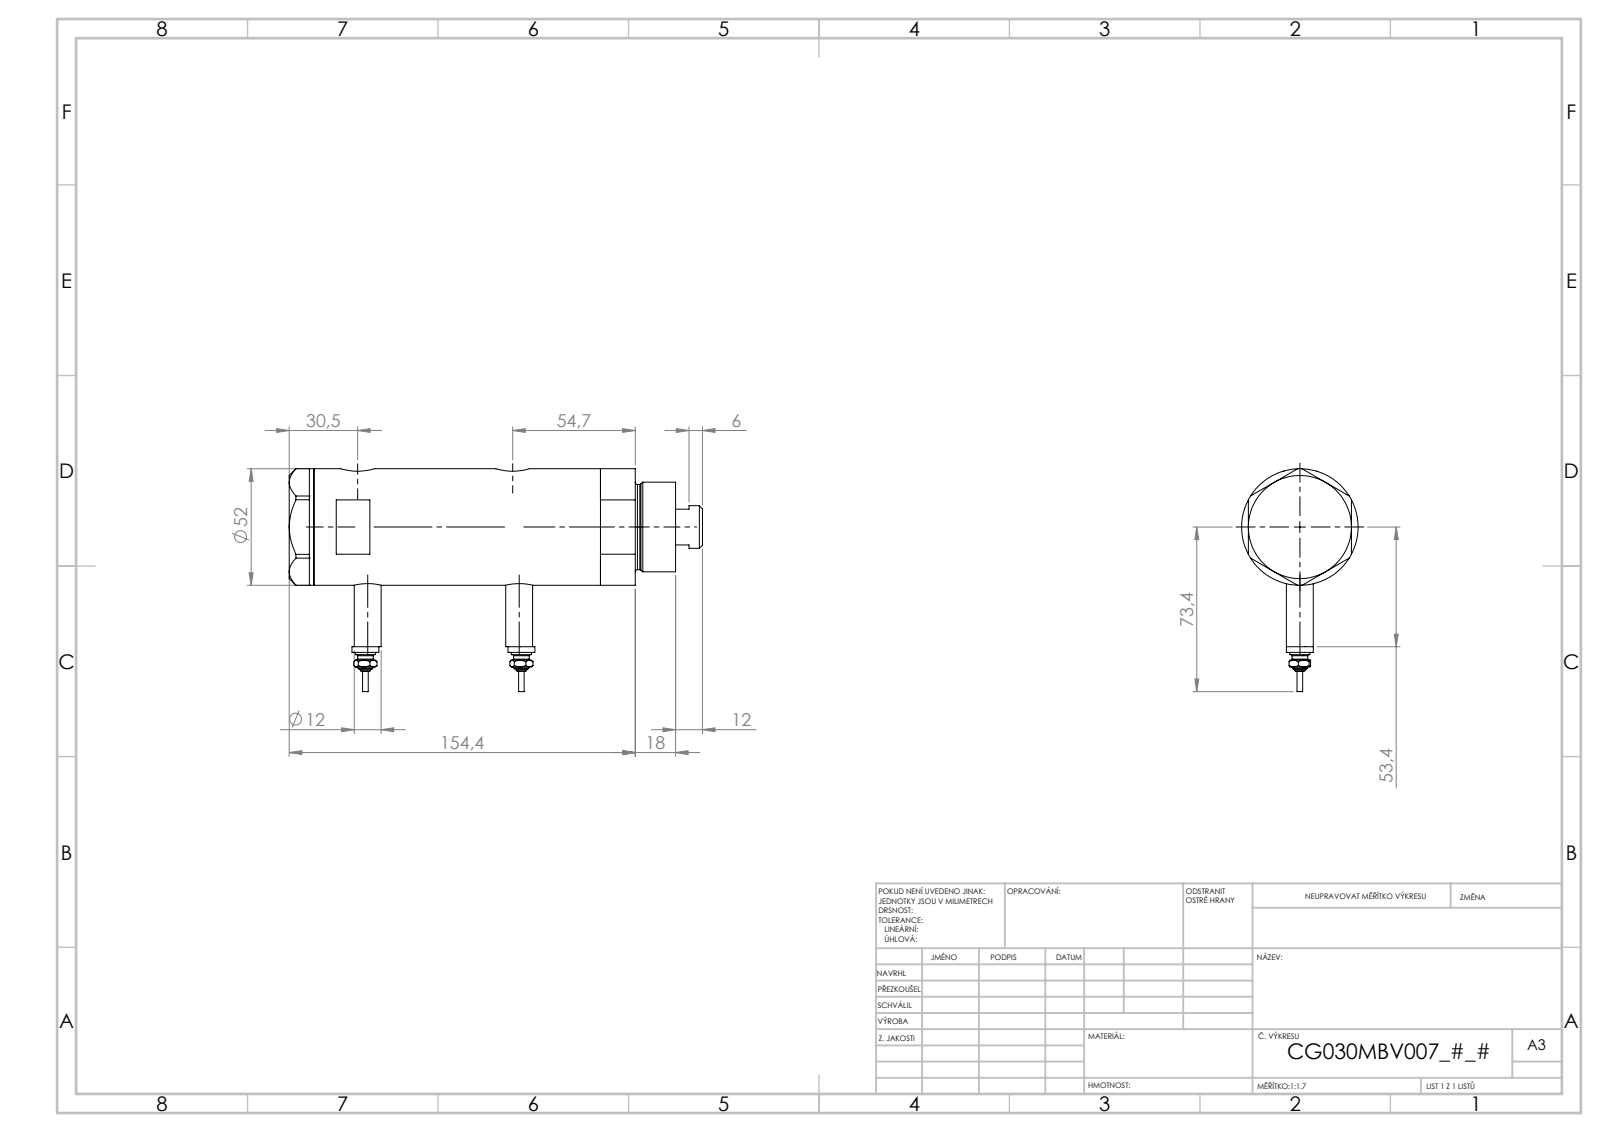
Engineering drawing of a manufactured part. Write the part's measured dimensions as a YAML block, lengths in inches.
part_name: "V270CG_MIDDLE; V270CG_BACK; V270CG_VC; Switch (+1 more)"
step_written_by: "SolidWorks 2019 (CONFIG_CONTROL_DESIGN)"
units: inches
bodies: {solids: 6, faces: 226, planar: 93, cylindrical: 69, other: 64}
overall_size: [7.26, 3.913, 2.047]
volume: 21.36
surface_area: 125
round_holes:
  - {diameter: 0.383, count: 2}
  - {diameter: 0.492, count: 2}
  - {diameter: 0.591, count: 2}
  - {diameter: 0.256, count: 1}
  - {diameter: 0.787, count: 1}
  - {diameter: 0.846, count: 1}
  - {diameter: 1.181, count: 1}
  - {diameter: 1.299, count: 1}
  - {diameter: 1.732, count: 1}
round_bosses_or_shafts:
  - {diameter: 0.472, count: 4}
  - {diameter: 0.354, count: 2}
  - {diameter: 0.276, count: 2}
  - {diameter: 0.177, count: 2}
  - {diameter: 0.098, count: 2}
  - {diameter: 2.047, count: 1}
  - {diameter: 1.575, count: 1}
  - {diameter: 1.496, count: 1}
face_to_face_distances: [3.602, 0.937, 2.665, 0.433, 1.37, 4.035, 1.811, 1.433, 5.469, 5.035]
hole_center_spacings: [0.114, 0.177, 2.547, 2.661, 2.724, 2.839]
